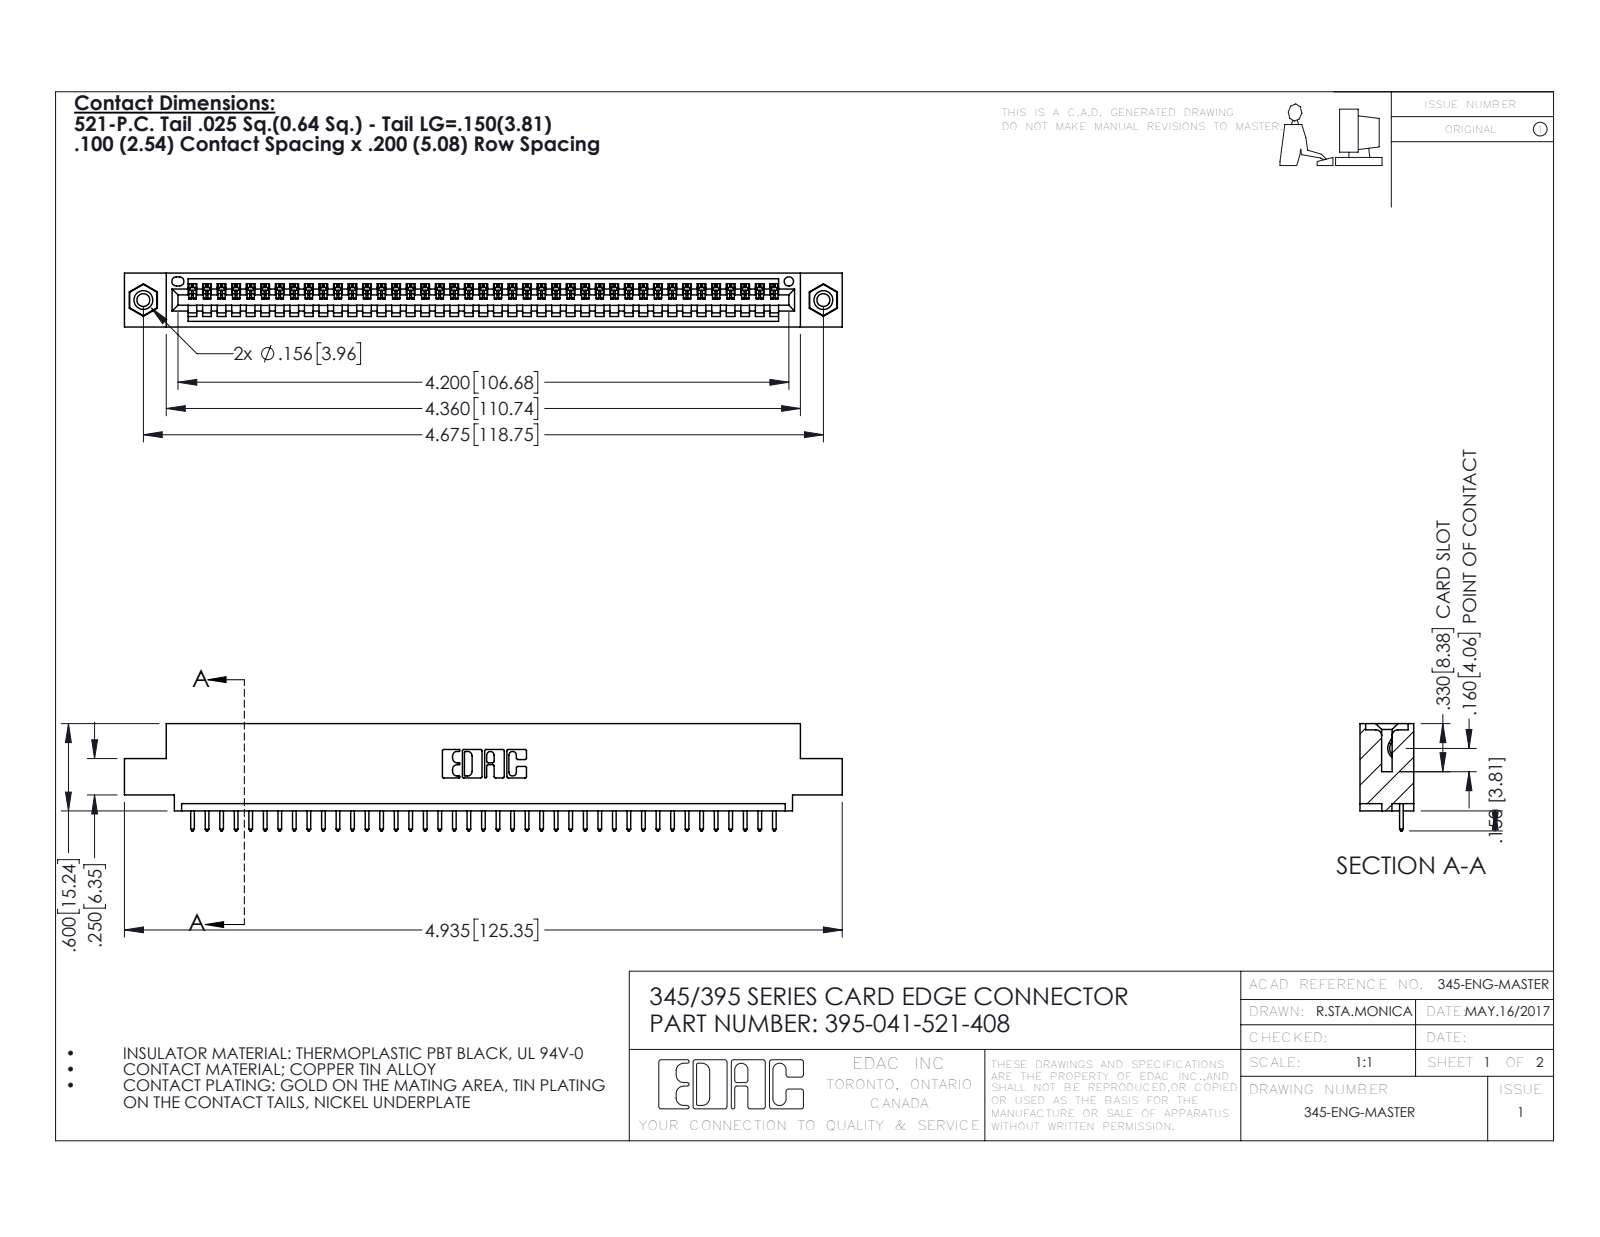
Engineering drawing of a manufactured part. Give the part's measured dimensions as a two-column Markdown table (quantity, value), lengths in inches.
| quantity | value |
| --- | --- |
| part name | 345 Part_0.110 Offset - 0.156 Dia-TI; 345-292-001_345-293-121; 395-041-521-408; 345-250-001_345-250-003-102 |
| STEP written by | SolidWorks 2016 (CONFIG_CONTROL_DESIGN) |
| units | inches |
| bodies | 44 solids, 2568 faces (1756 planar, 796 cylindrical, 16 other) |
| overall size | 4.935 × 0.737 × 0.37 |
| volume | 0.714 in³ |
| surface area | 23.53 in² |
| round holes (diameter × count) | 0.089 × 2, 0.125 × 2, 0.156 × 2, 0.064 × 1 |
| round bosses / shafts (diameter × count) | 0.155 × 2 |
| partial cylindrical surfaces (radius × count) | 0.006 × 82, 0.01 × 82, 0.01 × 22, 0.007 × 6, 0.031 × 6, 0.026 × 3, 0.031 × 2, 0.04 × 2 |
| main face-to-face distances | 0.072, 0.298, 0.37, 0.2, 0.098, 0.272, 0.025, 0.225, 0.149, 0.072 |
| hole center spacings | 0.27, 4.439, 4.675 |
